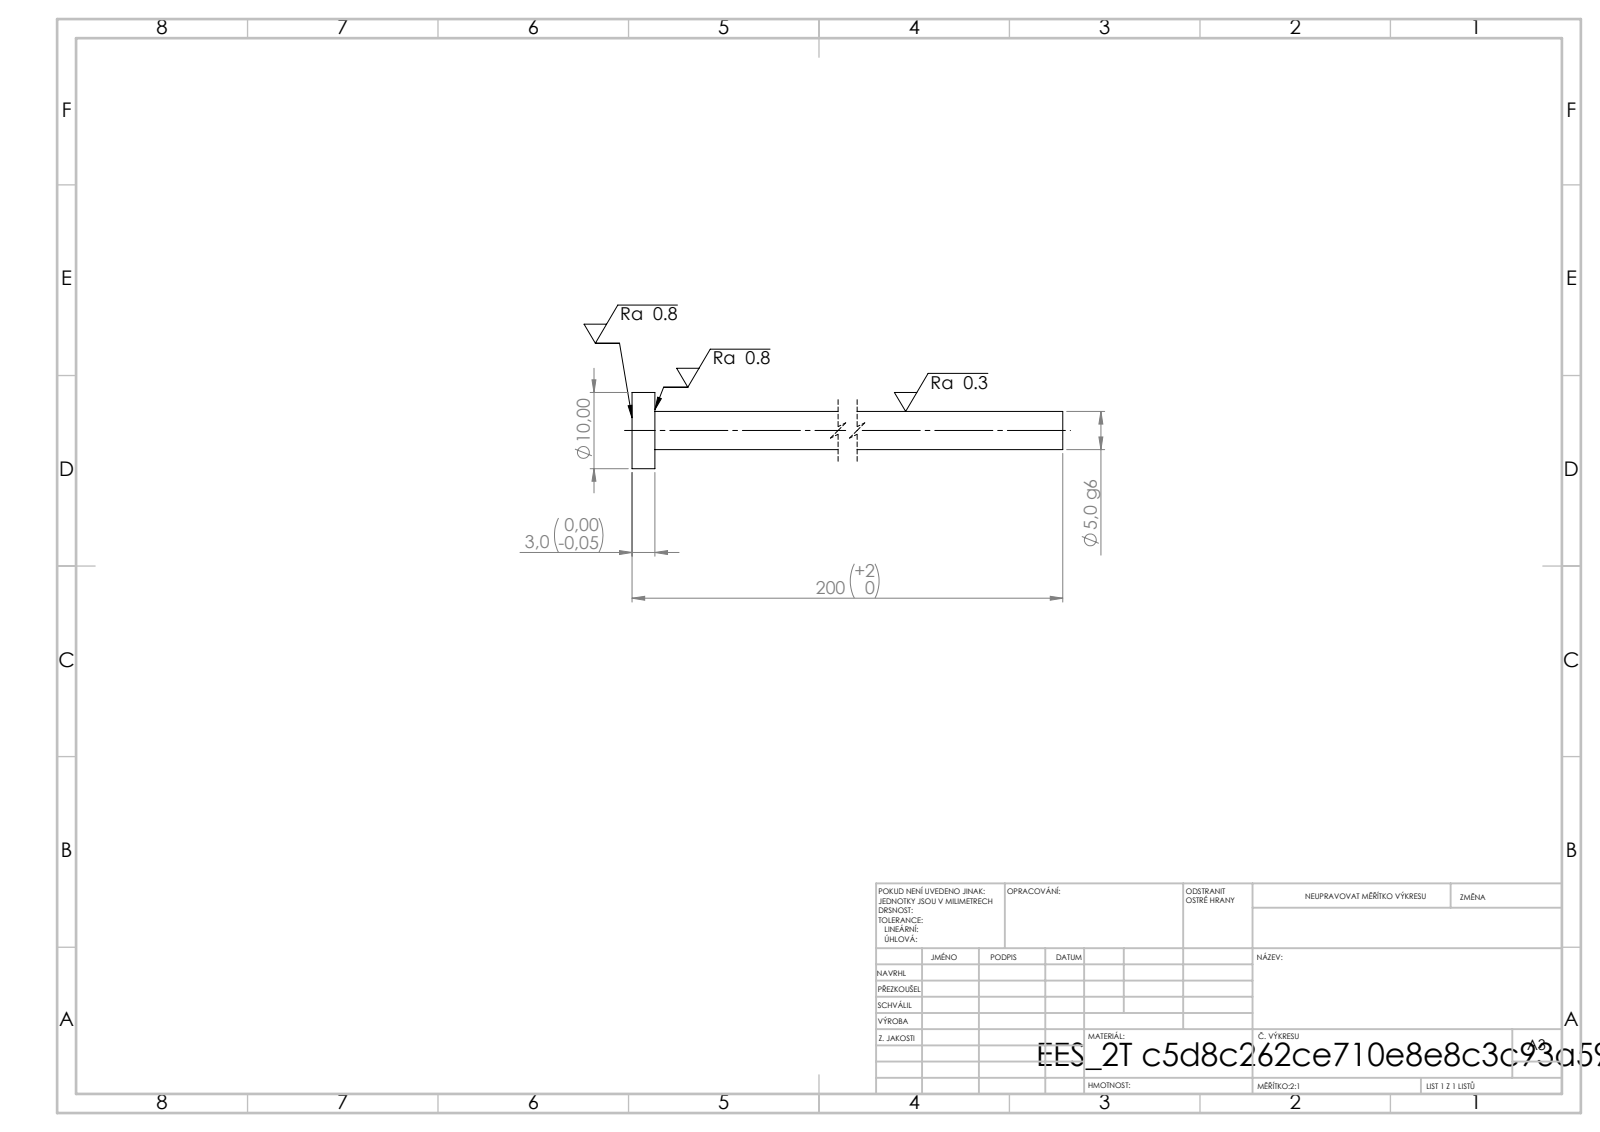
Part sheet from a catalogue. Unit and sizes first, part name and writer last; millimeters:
Units: millimetres
Overall size (bounding box): 200 × 10 × 10
Round bosses / shafts (diameter × count): ⌀10 ×1, ⌀5 ×1
Main face-to-face distances: 3, 200, 197
Volume: 4 104 mm³ · Surface area: 3 346 mm²
Bodies: 1 solid, 7 faces (3 planar, 4 cylindrical, 0 other)
STEP written by: SolidWorks 2019 (CONFIG_CONTROL_DESIGN)
